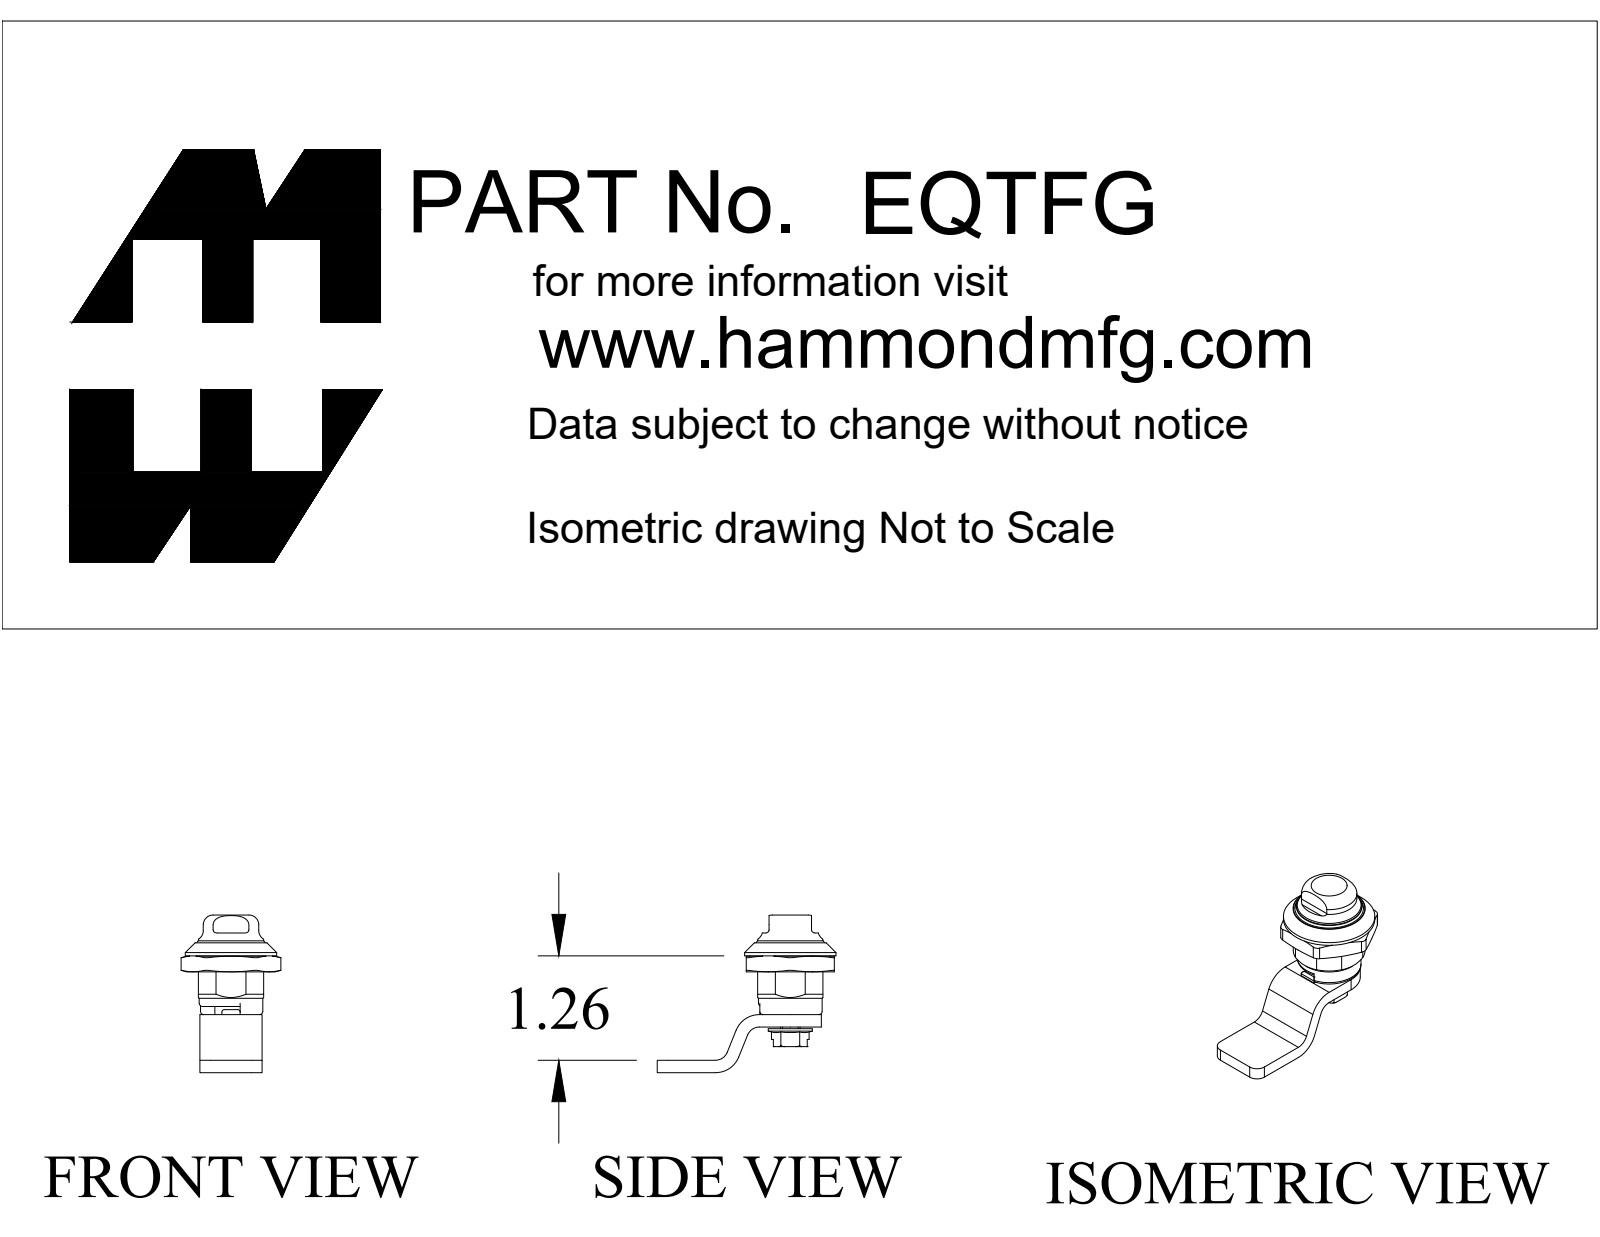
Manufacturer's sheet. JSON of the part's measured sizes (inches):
{"part_name": "EQTFG", "step_written_by": "SolidWorks 2019 (CONFIG_CONTROL_DESIGN)", "units": "inches", "bodies": {"solids": 7, "faces": 205, "planar": 107, "cylindrical": 50, "other": 48}, "overall_size": [2.156, 1.901, 1.203], "volume_in3": 0.933, "surface_area_in2": 17.65, "round_holes": [[0.194, 1], [0.358, 1], [0.394, 1], [0.524, 1], [0.634, 1], [0.802, 1], [0.827, 1]], "round_bosses_or_shafts": [[1.102, 1], [0.866, 1], [0.787, 1], [0.768, 1], [0.65, 1], [0.571, 1], [0.531, 1], [0.48, 1]], "partial_cylinders_radius": [[0.012, 8], [0.079, 6], [0.008, 4], [0.03, 4], [0.039, 2], [0.125, 2], [0.15, 2], [0.3, 2]], "face_to_face_distances": [0.15, 0.55, 0.374, 0.7, 0.787, 0.098, 0.4, 0.709, 0.236, 0.181]}
